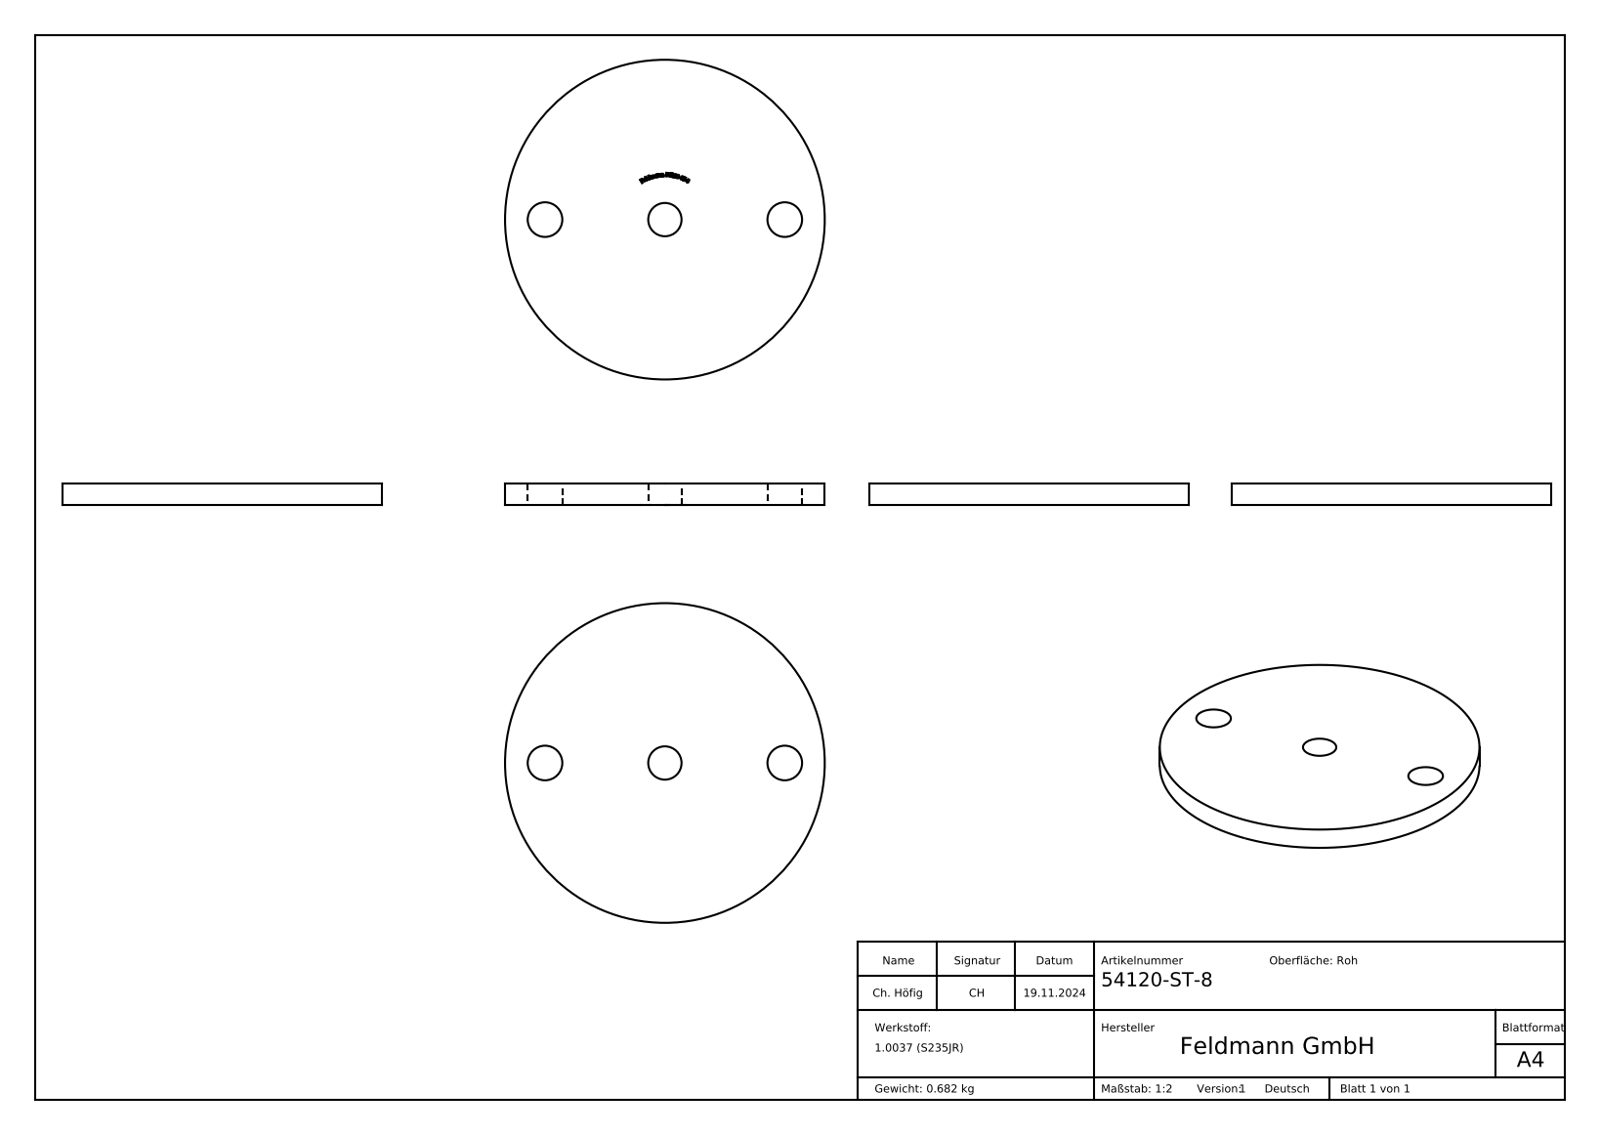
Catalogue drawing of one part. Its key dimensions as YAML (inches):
part_name: "54120-ST-8"
step_written_by: "SolidWorks 2018 (CONFIG_CONTROL_DESIGN)"
units: inches
bodies: {solids: 1, faces: 237, planar: 130, cylindrical: 4, other: 103}
overall_size: [4.724, 4.724, 0.315]
volume: 5.332
surface_area: 40.05
round_holes:
  - {diameter: 0.512, count: 2}
  - {diameter: 0.492, count: 1}
round_bosses_or_shafts:
  - {diameter: 4.724, count: 1}
face_to_face_distances: [0.315, 0.311, 0.021, 0.026, 0.028, 0.052, 0.026, 0.031, 0.057, 0.047]
hole_center_spacings: [1.772, 3.543]
